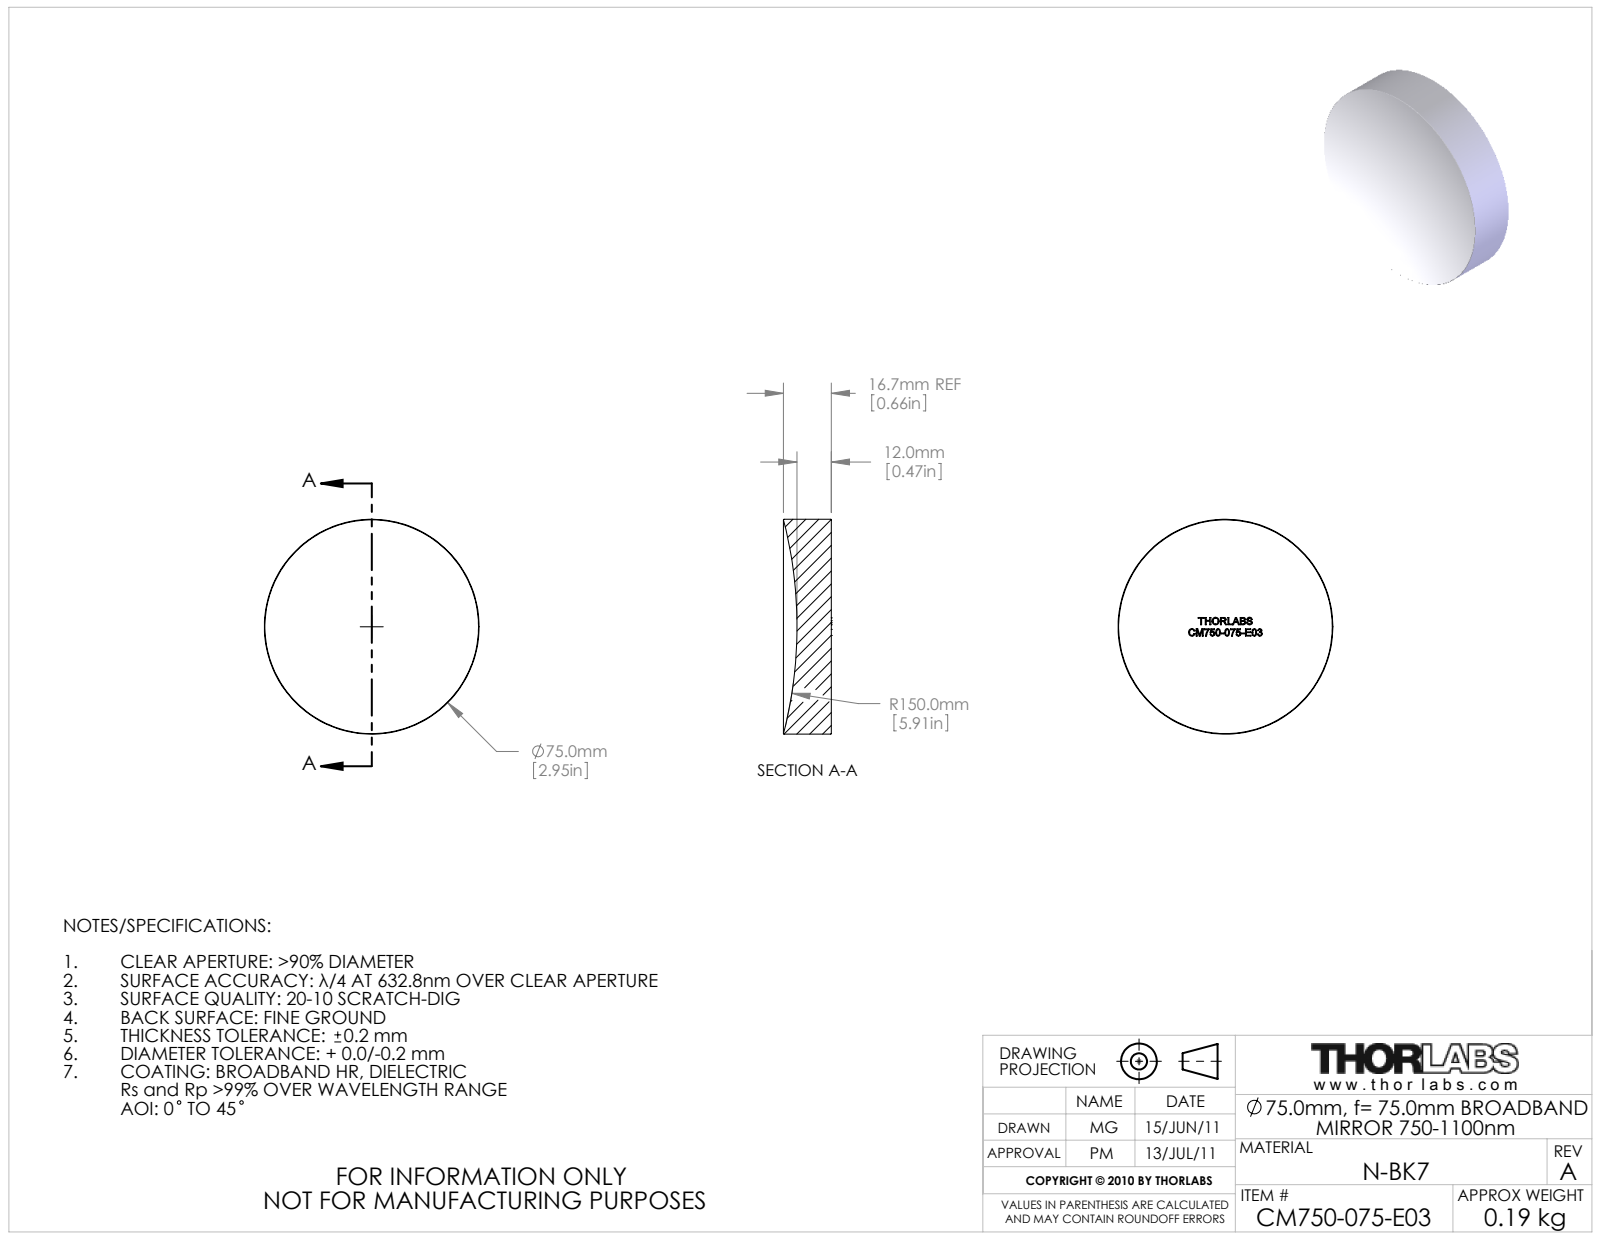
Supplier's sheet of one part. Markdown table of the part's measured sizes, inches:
| quantity | value |
| --- | --- |
| part name | 22649-E0W |
| STEP written by | SolidWorks 2011 (AUTOMOTIVE_DESIGN) |
| units | inches |
| bodies | 0 solids, 38 faces (30 planar, 2 cylindrical, 6 other) |
| overall size | 2.953 × 2.953 × 0.658 |
| round bosses / shafts (diameter × count) | 2.953 × 1 |
